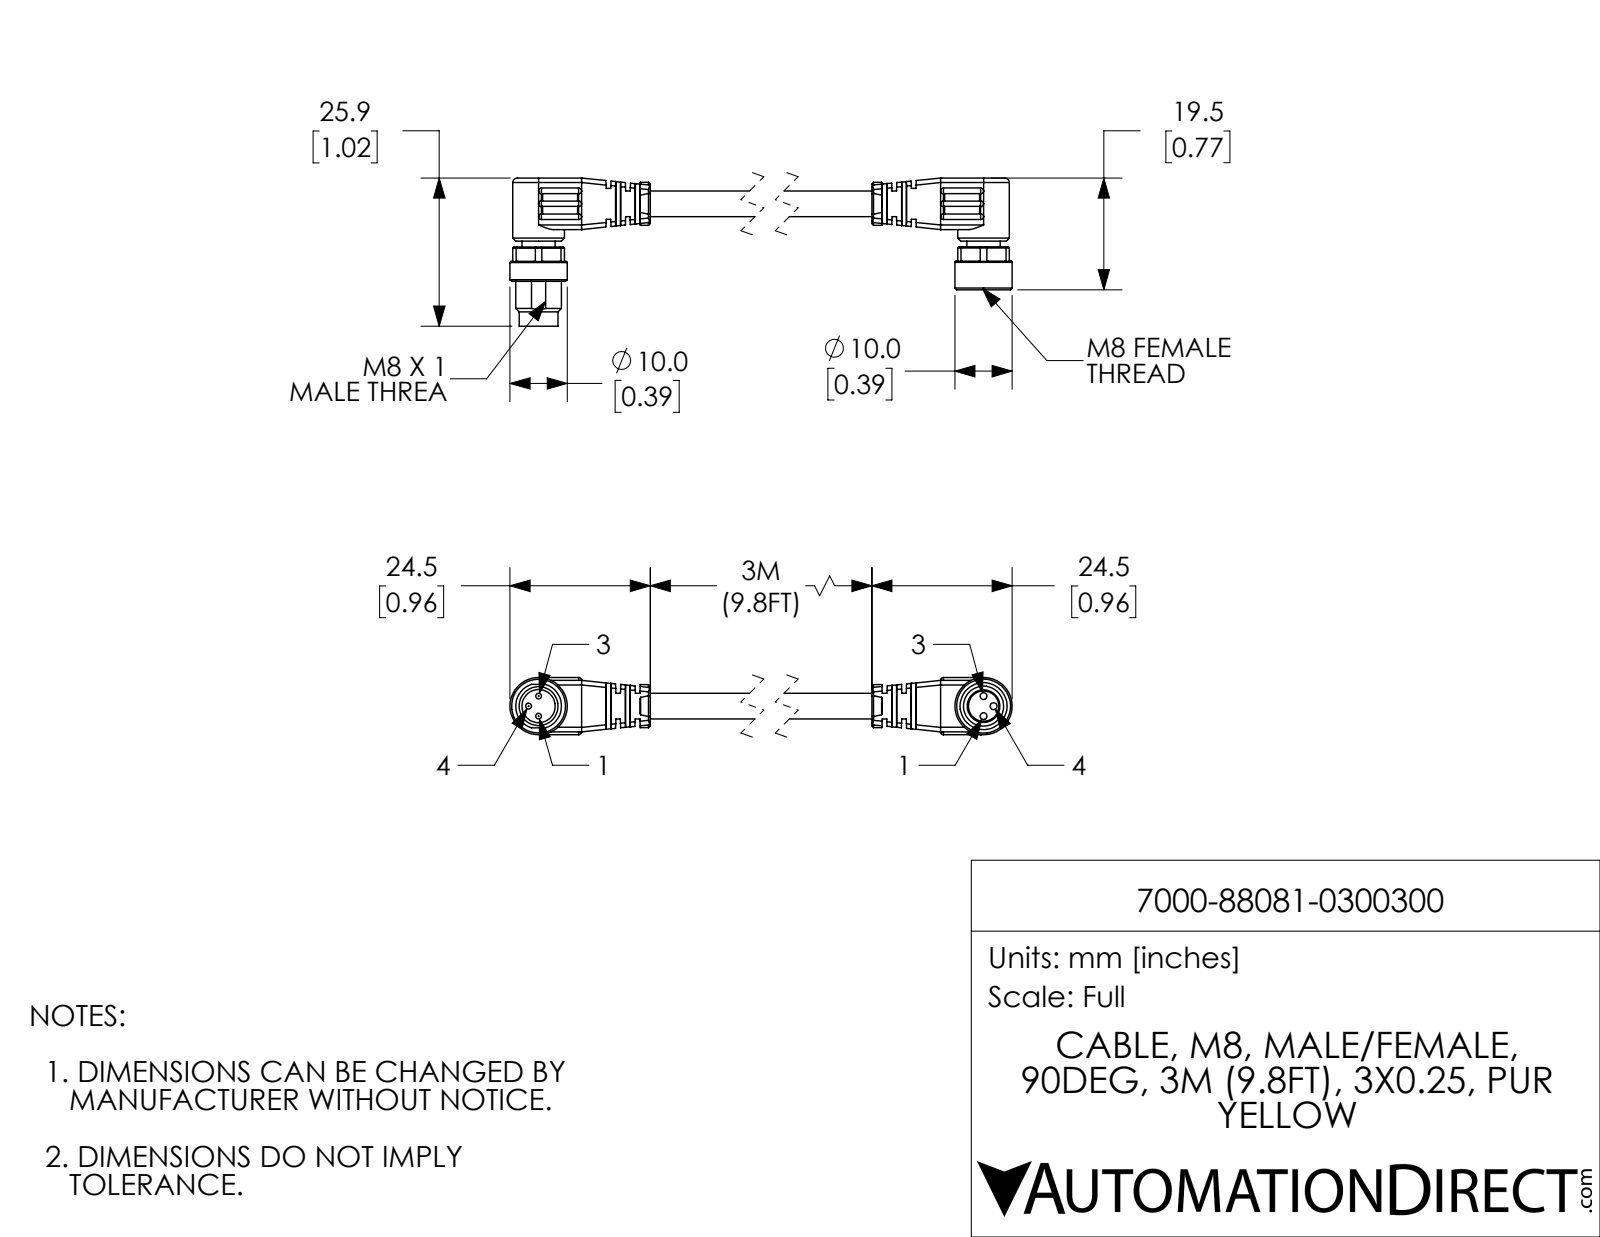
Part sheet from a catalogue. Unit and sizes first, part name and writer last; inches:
Units: inches
Overall size (bounding box): 3.976 × 1.018 × 0.394
Round holes (diameter × count): ⌀0.047 ×3, ⌀0.228 ×1, ⌀0.276 ×1
Round bosses / shafts (diameter × count): ⌀0.039 ×3, ⌀0.394 ×2, ⌀0.354 ×2, ⌀0.315 ×1, ⌀0.268 ×1, ⌀0.228 ×1, ⌀0.224 ×1, ⌀0.177 ×1
Partial cylindrical surfaces — rounded edges, fillets, slot ends (radius × count): R0.031 ×12, R0.008 ×8, R0.02 ×6, R0.193 ×2, R0.148 ×1
Main face-to-face distances: 0.041, 0.354, 0.042, 0.266, 0.362, 0.089, 0.024, 0.133, 0.472, 2.353
Hole centre spacings: 0.069, 0.097, 3.583, 0.138, 3.583, 3.652
Volume: 0.317 in³ · Surface area: 6.059 in²
Bodies: 2 solids, 410 faces (190 planar, 144 cylindrical, 76 other)
Part name (STEP PRODUCT): 7000-88081-0300300; 7000-88081-0300300_MALE; 7000-88081-0300300_FEMALE
STEP written by: SolidWorks 2021 (CONFIG_CONTROL_DESIGN)
